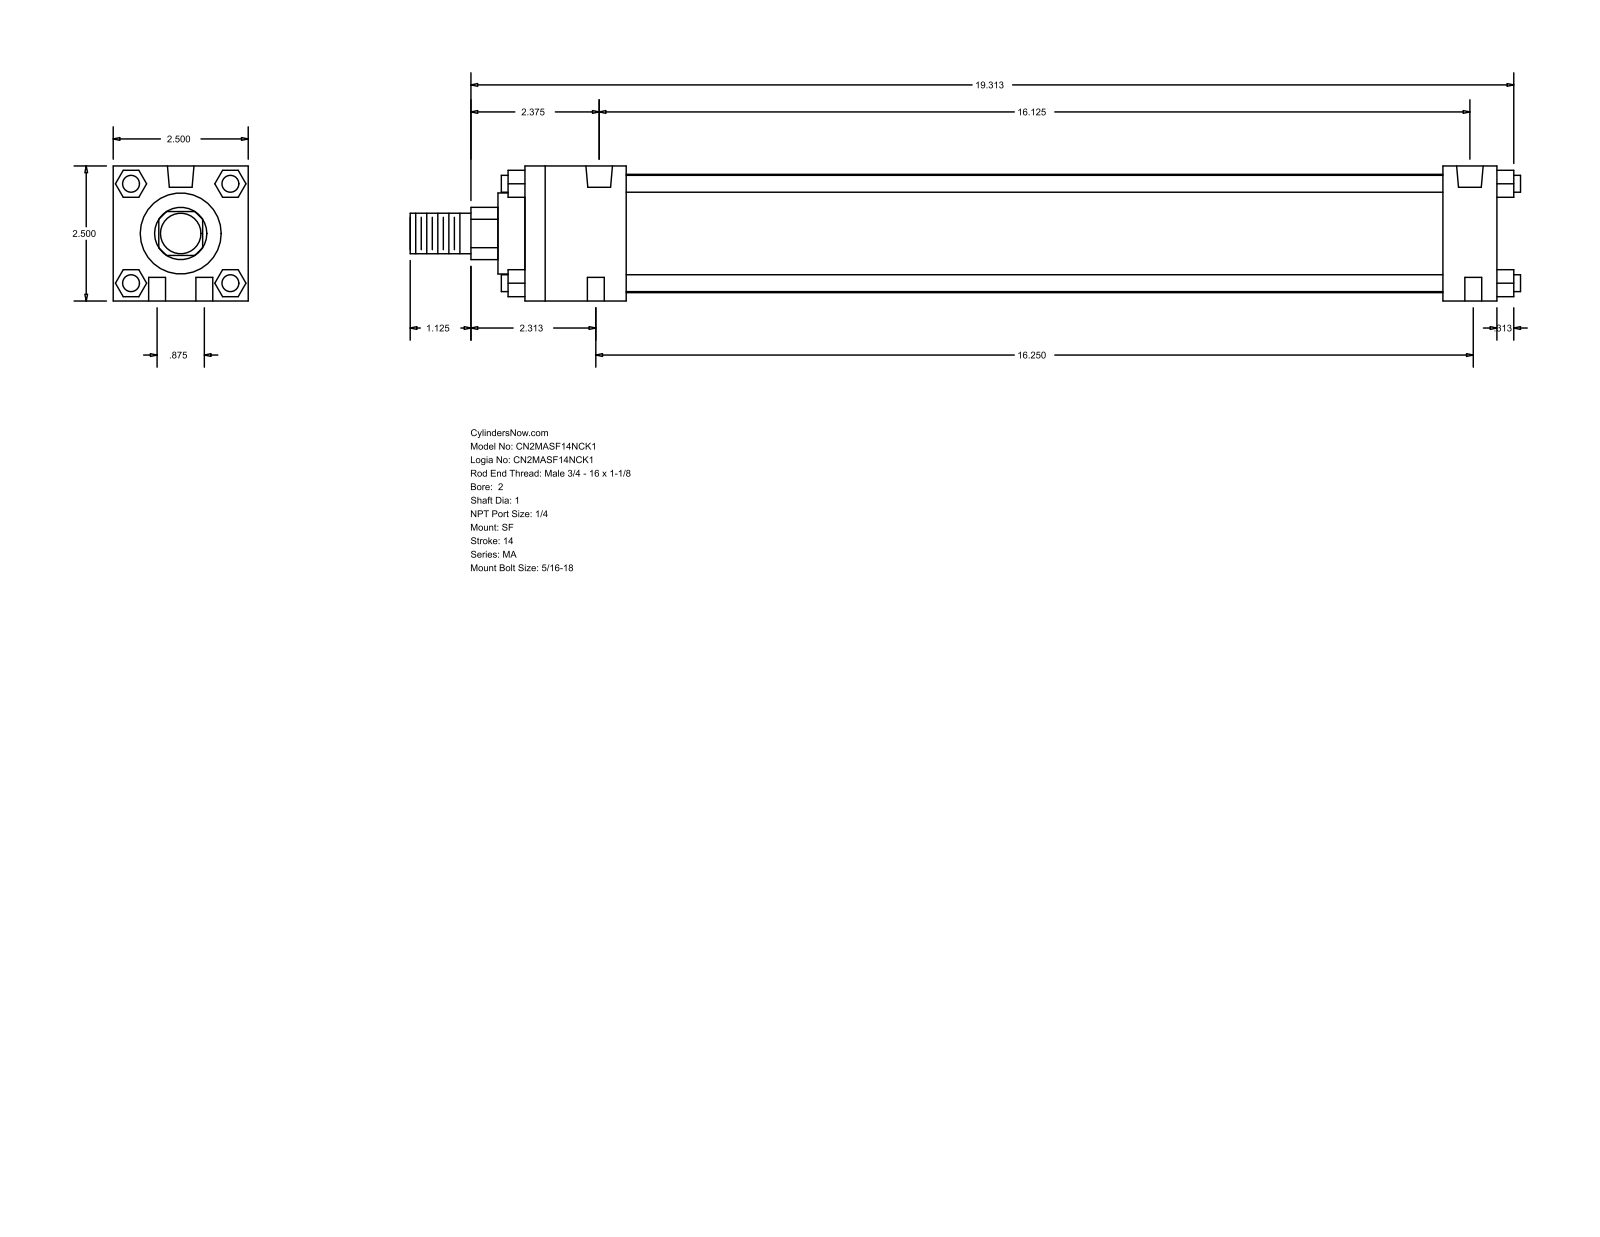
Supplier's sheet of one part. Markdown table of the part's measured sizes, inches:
| quantity | value |
| --- | --- |
| part name | MA_SF__0200_1 |
| STEP written by | GSSL Pune (CONFIG_CONTROL_DESIGN) |
| units | inches |
| bodies | 0 solids, 124 faces (94 planar, 30 cylindrical, 0 other) |
| overall size | 20.563 × 2.5 × 2.5 |
| round holes (diameter × count) | 0.313 × 6, 0.492 × 2 |
| round bosses / shafts (diameter × count) | 0.313 × 4, 2.19 × 1, 1.5 × 1, 1 × 1, 0.75 × 1 |
| partial cylindrical surfaces (radius × count) | 0.484 × 1 |
| main face-to-face distances | 2.5, 18, 0.5, 1, 17, 1.875, 15.125, 16.125, 0.92, 1.593 |
| hole center spacings | 0.442, 16.193, 0.875, 16.125, 16.25, 16.274 |
